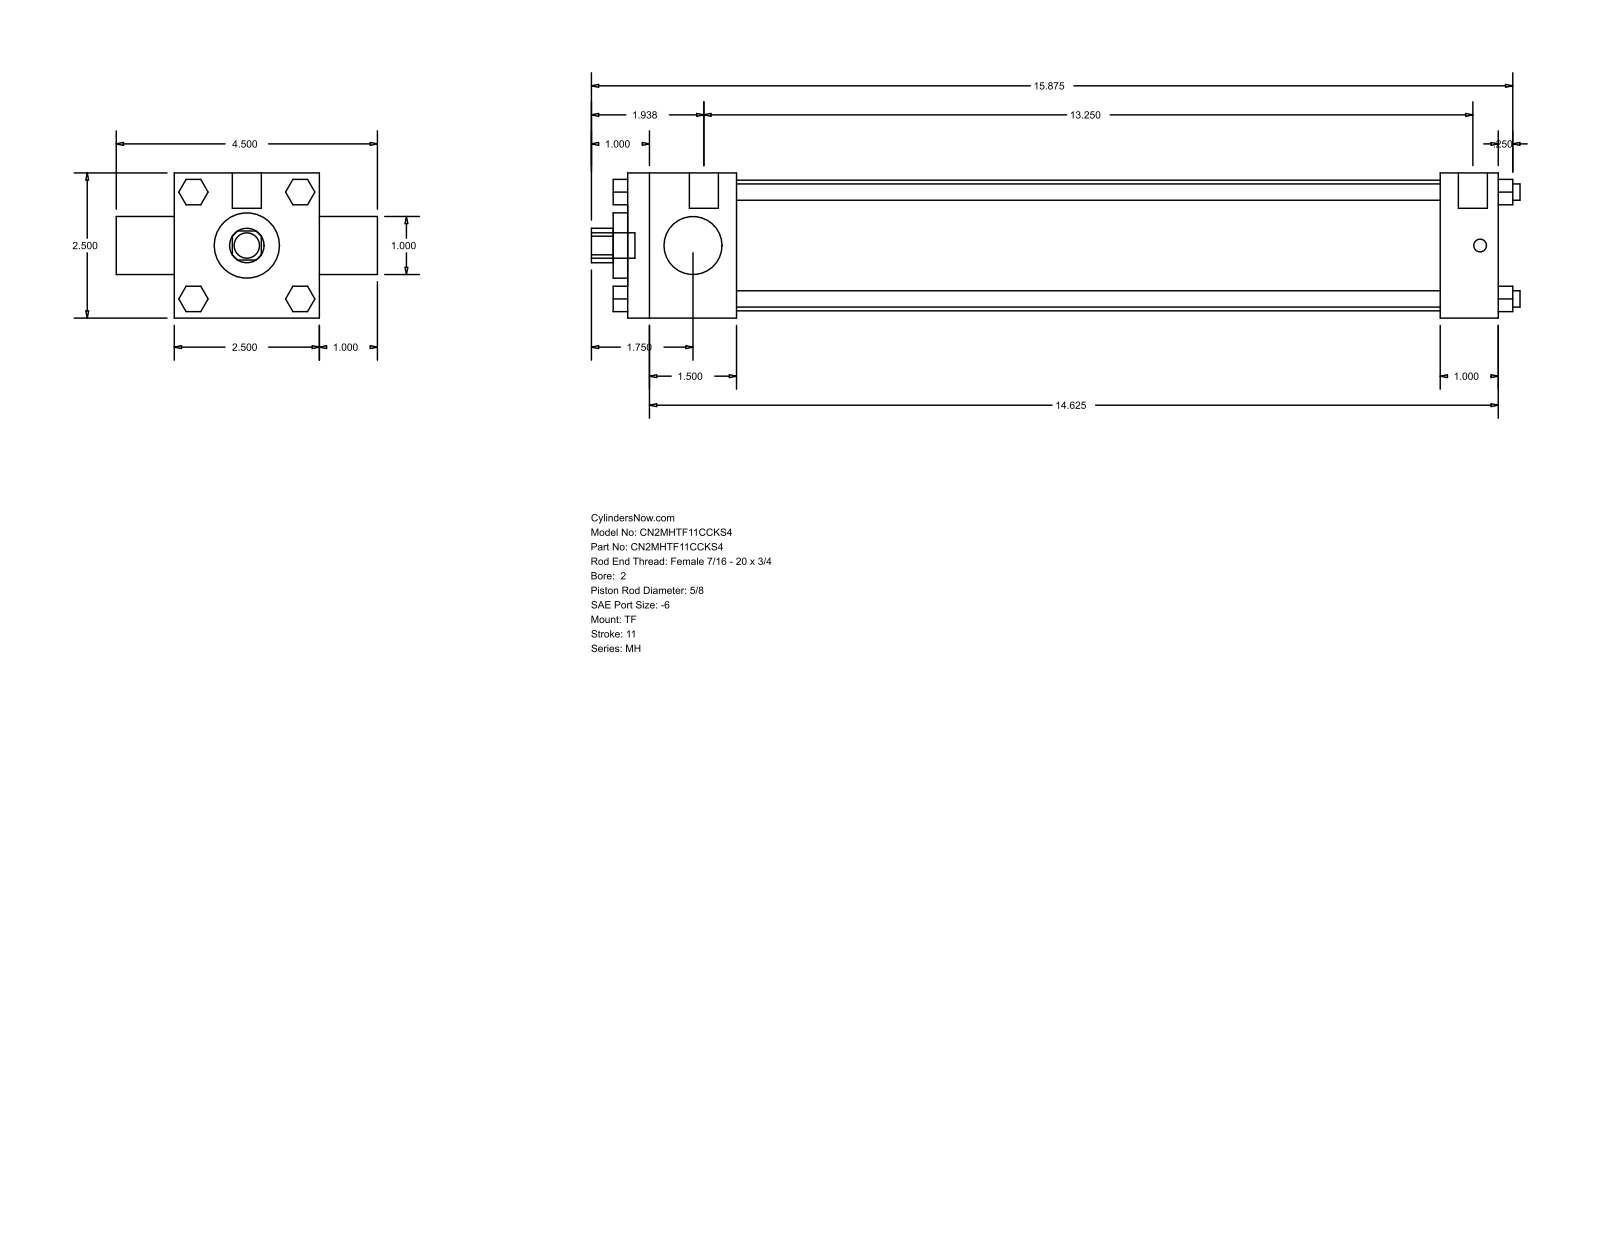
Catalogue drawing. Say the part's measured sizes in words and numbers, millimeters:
The part is named "MH_TF__0200_0.625". Its 3-D file was written by "GSSL Pune (CONFIG_CONTROL_DESIGN)". It is 0 solids with 120 faces: 92 planar, 28 cylindrical and 0 other. Overall it measures 406.4 by 114.3 by 63.5 millimeters. Round holes: 1 of diameter 15.88, 1 of diameter 25.4, 1 of diameter 28.57, 1 of diameter 57.15. Round bosses or shafts: 4 of diameter 7.14, 3 of diameter 5.56, 2 of diameter 12.7, 1 of diameter 11.11. Partial cylindrical surfaces (rounded edges, fillets, slot ends): 1 of radius 7.54. The main face-to-face distances are 63.5, 381, 25.4, 47.62, 355.6, 307.98, 333.38, 387.35, 6.35, 88.9.
